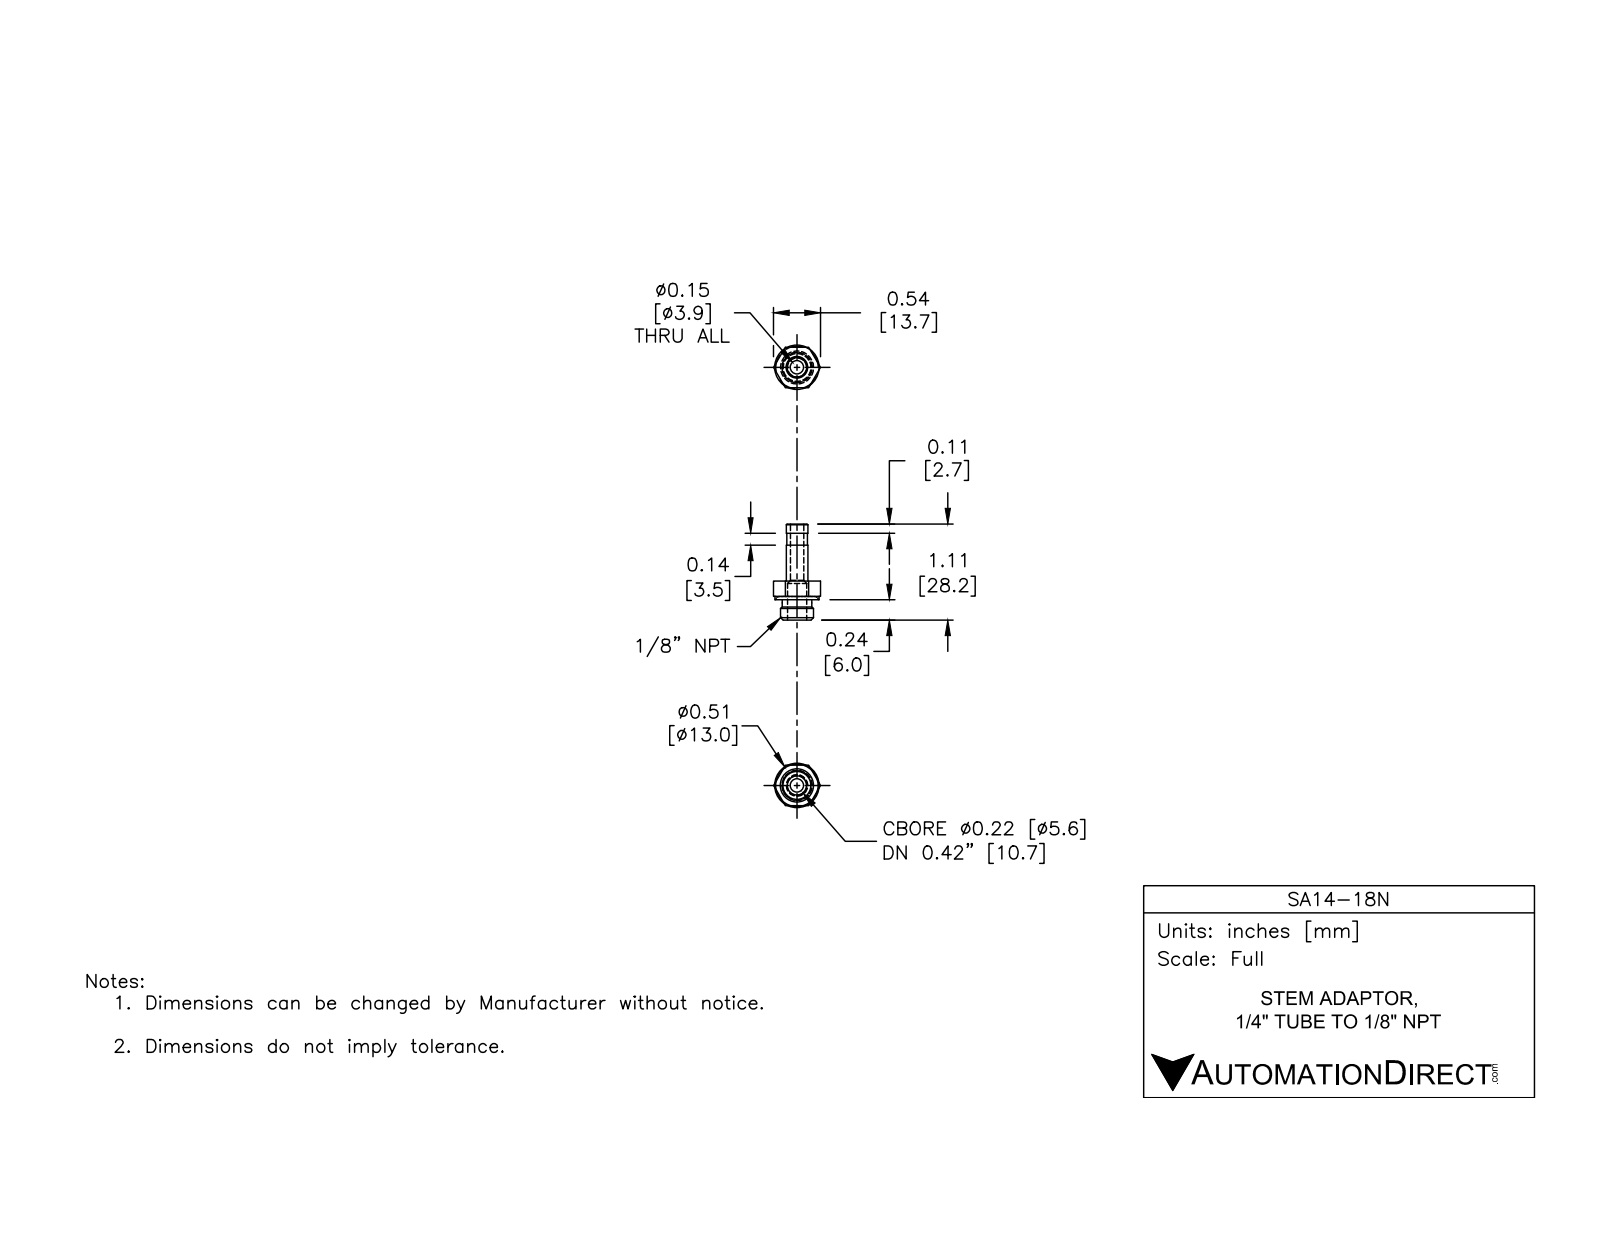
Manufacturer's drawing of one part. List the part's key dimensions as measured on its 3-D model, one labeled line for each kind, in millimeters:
Part name (STEP PRODUCT): SA14-18N
STEP written by: SolidWorks 2015 (CONFIG_CONTROL_DESIGN)
Units: millimetres
Bodies: 2 solids, 52 faces (24 planar, 16 cylindrical, 12 other)
Overall size (bounding box): 28.18 × 13.74 × 12.95
Volume: 1 195 mm³ · Surface area: 1 569 mm²
Round holes (diameter × count): ⌀3.91 ×1, ⌀5.63 ×1
Round bosses / shafts (diameter × count): ⌀12.95 ×1, ⌀9.68 ×1, ⌀8.72 ×1, ⌀6.32 ×1, ⌀6.02 ×1
Main face-to-face distances: 11.9, 5.46, 5.97, 11.43, 28.18, 22.21, 16.75, 6.99, 1.02, 4.44
